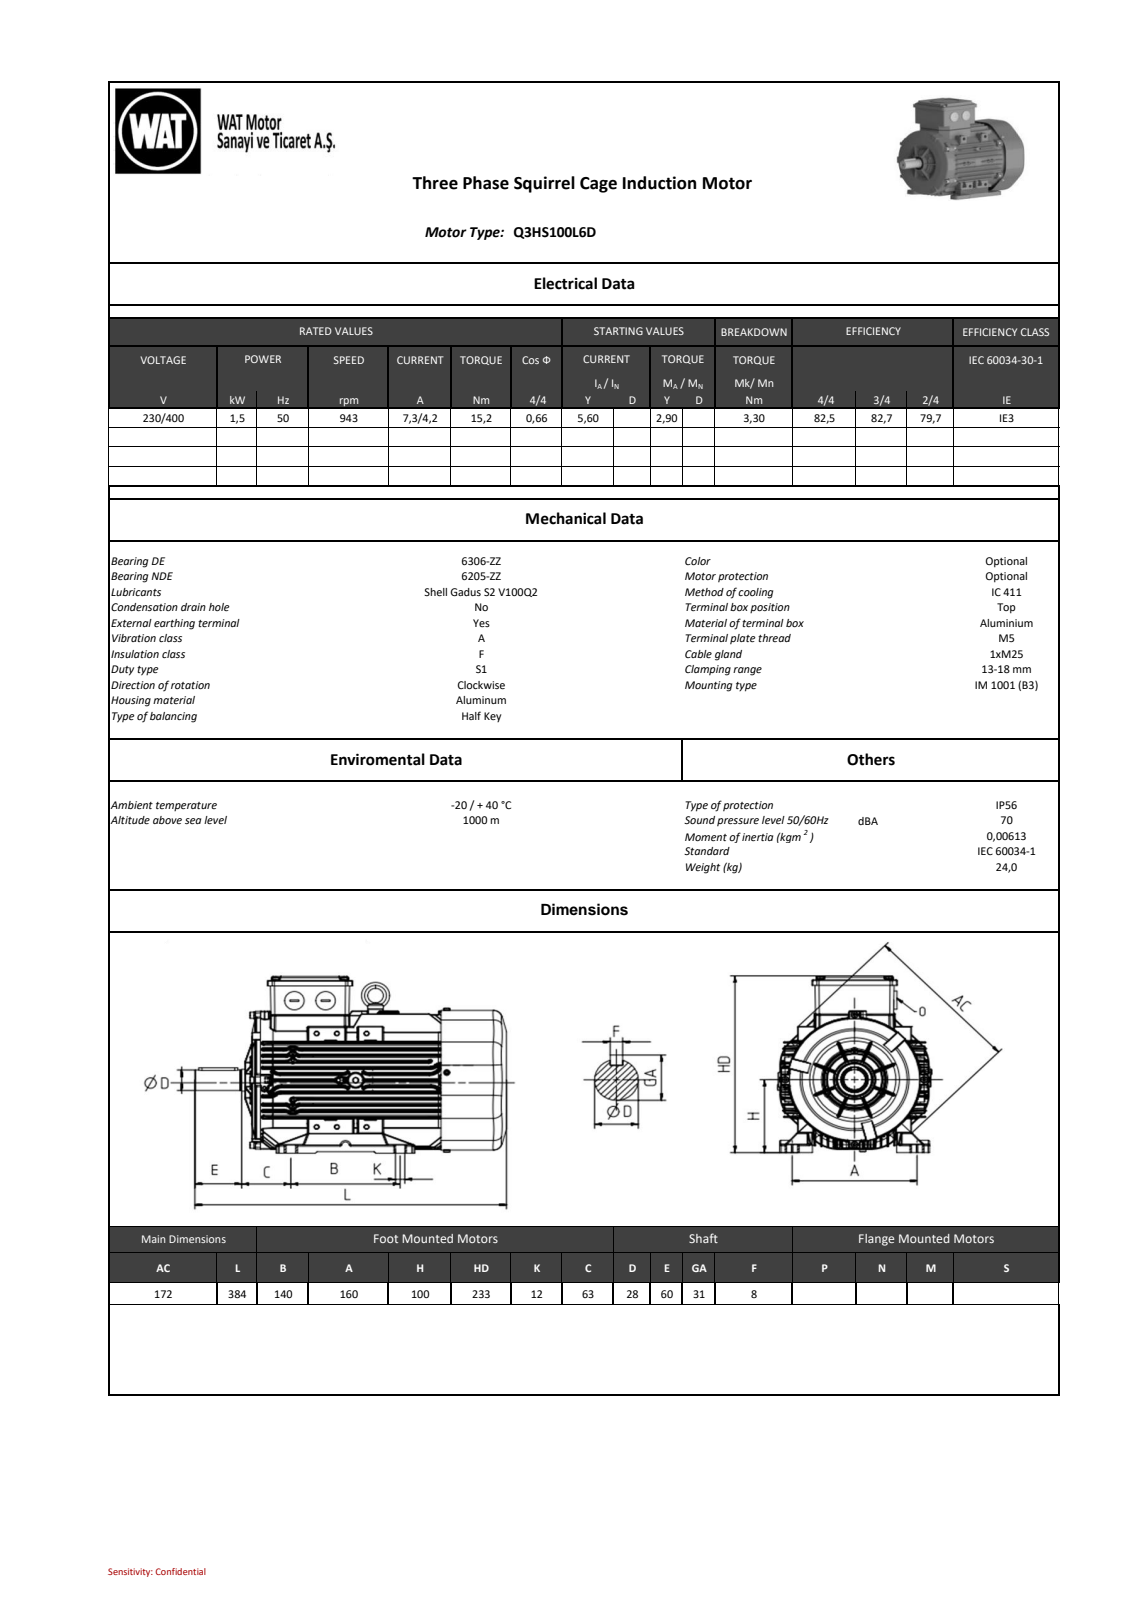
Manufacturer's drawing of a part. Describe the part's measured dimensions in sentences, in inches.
The part is named "QHS Series_ 100_B3 DEEP COVER_stp_objects". Its 3-D file was written by "SIEMENS PLM Software NX2206.8101 (AUTOMOTIVE_DESIGN)". It is 0 solids with 7129 faces: 1791 planar, 3180 cylindrical and 2158 other. Overall it measures 15.116 by 9.215 by 7.315 inches. Round holes: 3 of diameter 0.138, 1 of diameter 0.389, 1 of diameter 0.413, 1 of diameter 3.141, 1 of diameter 3.85, 1 of diameter 4.558. Round bosses or shafts: 8 of diameter 0.335, 7 of diameter 0.315, 4 of diameter 0.366, 4 of diameter 0.362, 4 of diameter 0.197, 2 of diameter 0.984, 1 of diameter 4.023, 1 of diameter 3.315. Partial cylindrical surfaces (rounded edges, fillets, slot ends): 639 of radius 0.039, 622 of radius 0.031, 599 of radius 0.02, 88 of radius 0.079, 28 of radius 0.315, 24 of radius 0.024, 10 of radius 0.157, 9 of radius 0.031. The main face-to-face distances are 0.295, 3.619, 0.352, 3.267, 0.928, 8.11, 0.29, 1.982, 3.557, 0.664. The hole center spacings are 1.535, 2.66, 1.527, 1.538, 1.542, 2.659.
